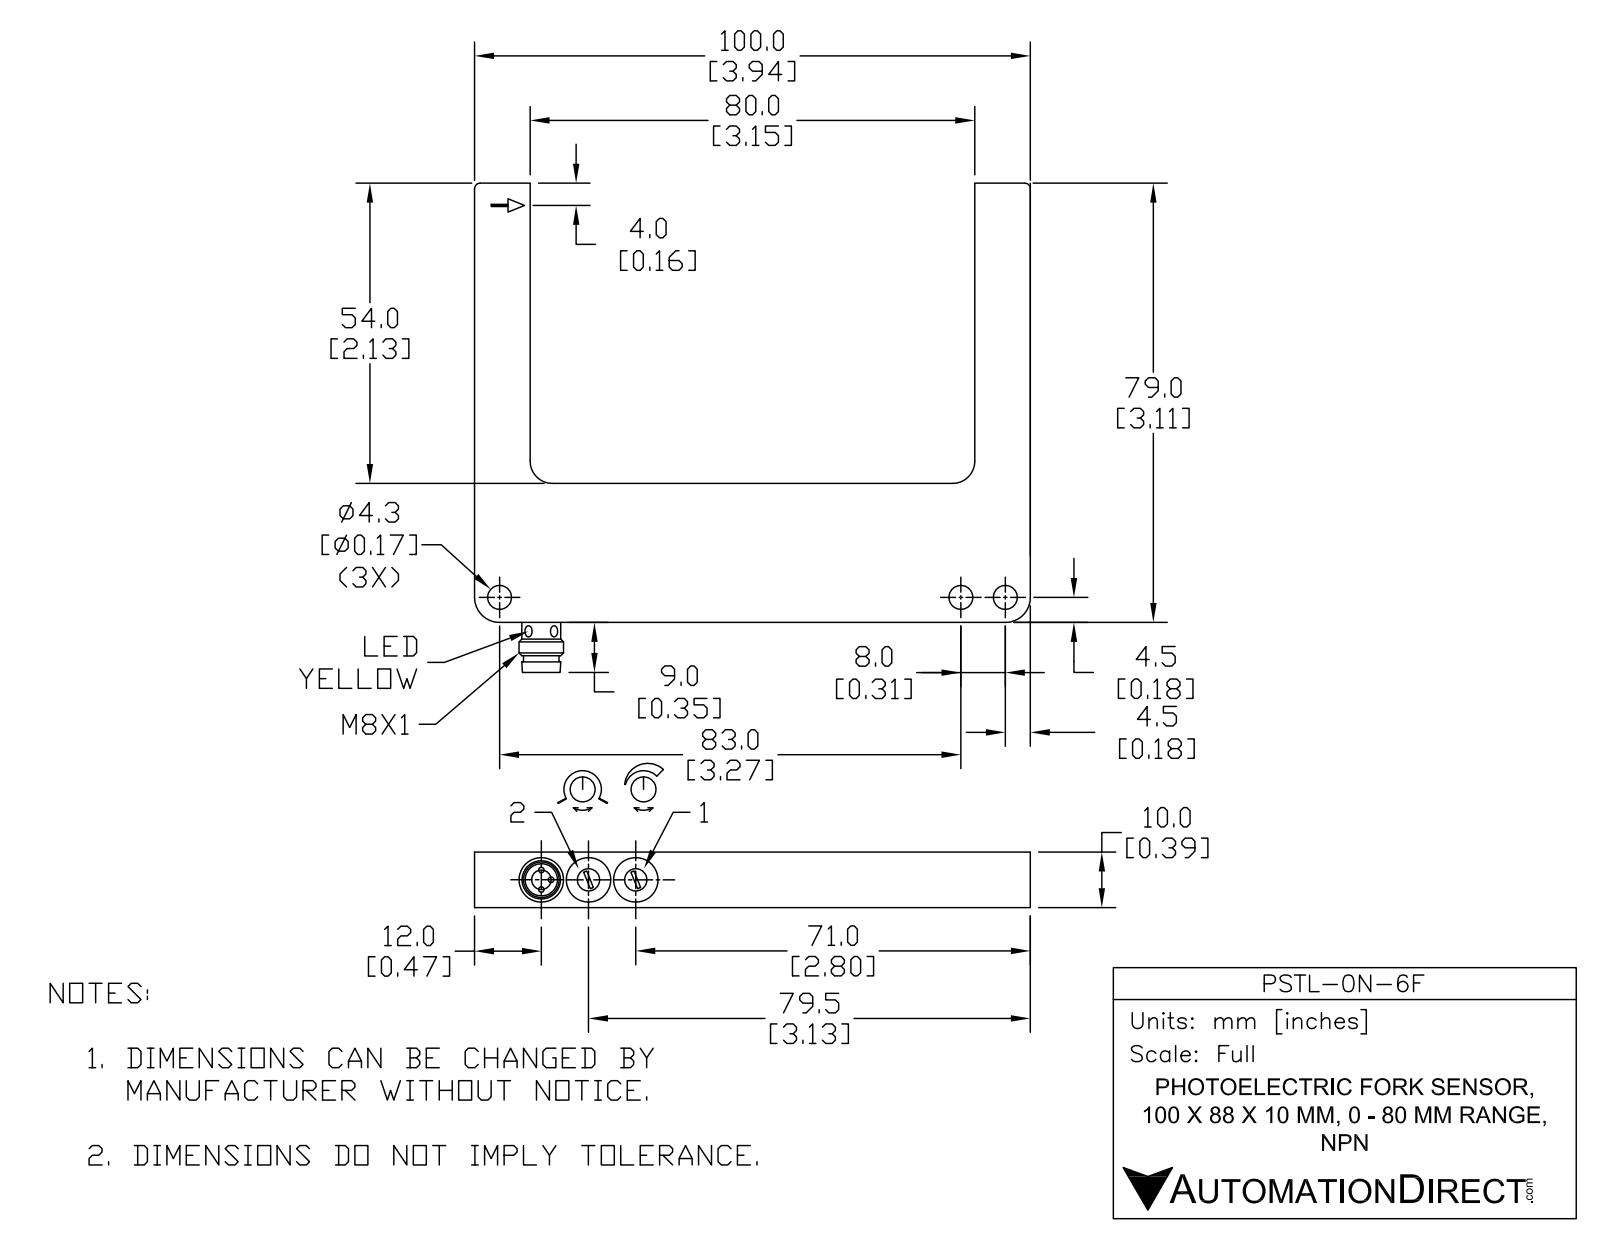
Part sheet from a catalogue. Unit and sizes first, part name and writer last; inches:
Units: inches
Overall size (bounding box): 3.937 × 3.465 × 0.394
Round holes (diameter × count): ⌀0.169 ×3, ⌀0.079 ×2, ⌀0.157 ×2, ⌀0.315 ×2, ⌀0.228 ×1
Round bosses / shafts (diameter × count): ⌀0.039 ×3, ⌀0.315 ×1, ⌀0.267 ×1
Partial cylindrical surfaces — rounded edges, fillets, slot ends (radius × count): R0.02 ×2, R0.039 ×2, R0.063 ×2, R0.157 ×2, R0.177 ×2
Main face-to-face distances: 0.394, 3.543, 3.937, 0.984, 3.15, 2.126, 3.11, 3.106, 0.98, 0.157
Hole centre spacings: 0.335, 0.315, 0.669, 3.268, 3.583
Volume: 2.17 in³ · Surface area: 19.25 in²
Bodies: 1 solid, 95 faces (35 planar, 48 cylindrical, 12 other)
Part name (STEP PRODUCT): PSTL-0N-6F
STEP written by: SolidWorks 2019 (AUTOMOTIVE_DESIGN)
